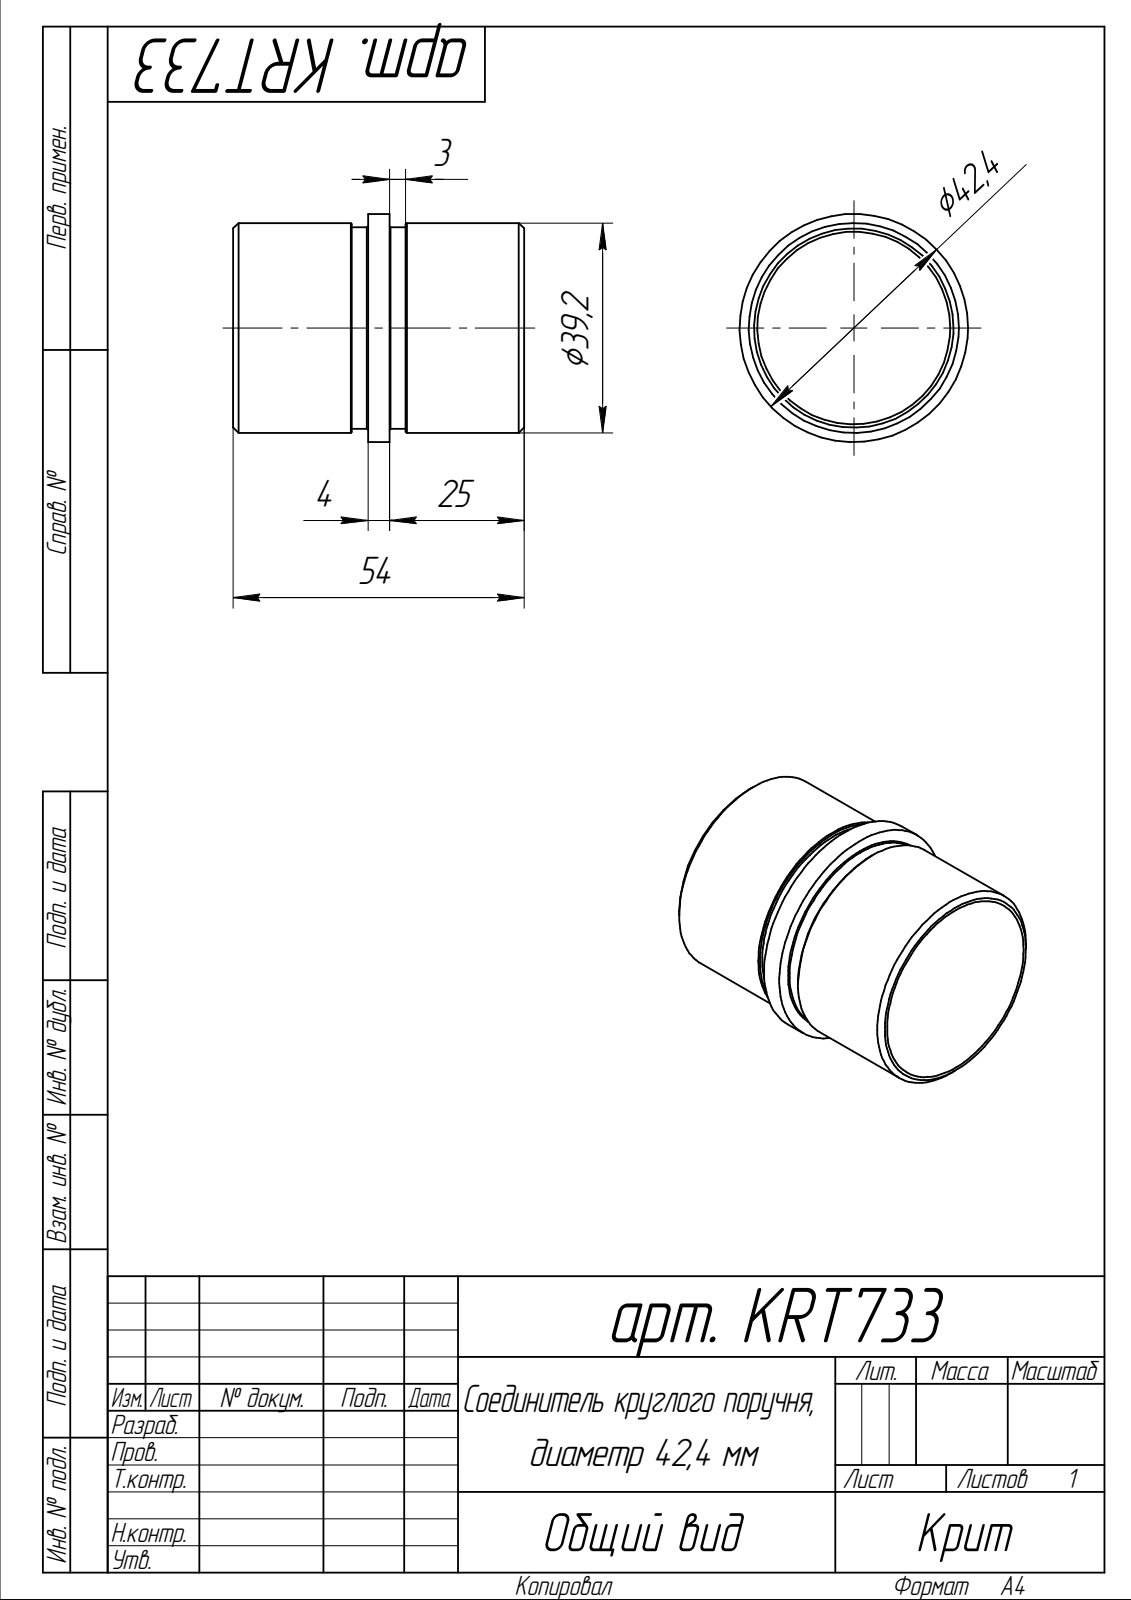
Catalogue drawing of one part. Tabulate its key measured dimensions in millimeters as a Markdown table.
| quantity | value |
| --- | --- |
| part name | арт. KRT733 |
| STEP written by | SolidWorks 2014 (AUTOMOTIVE_DESIGN) |
| units | millimeters |
| bodies | 1 solid, 30 faces (6 planar, 12 cylindrical, 12 other) |
| overall size | 54 × 42.4 × 42.4 |
| volume | 10 324 mm³ |
| surface area | 13 694 mm² |
| round holes (diameter × count) | 35.8 × 1 |
| round bosses / shafts (diameter × count) | 42.4 × 1, 39 × 1, 37.4 × 1 |
| main face-to-face distances | 4, 3, 7, 22, 25, 29, 32, 10, 54 |
